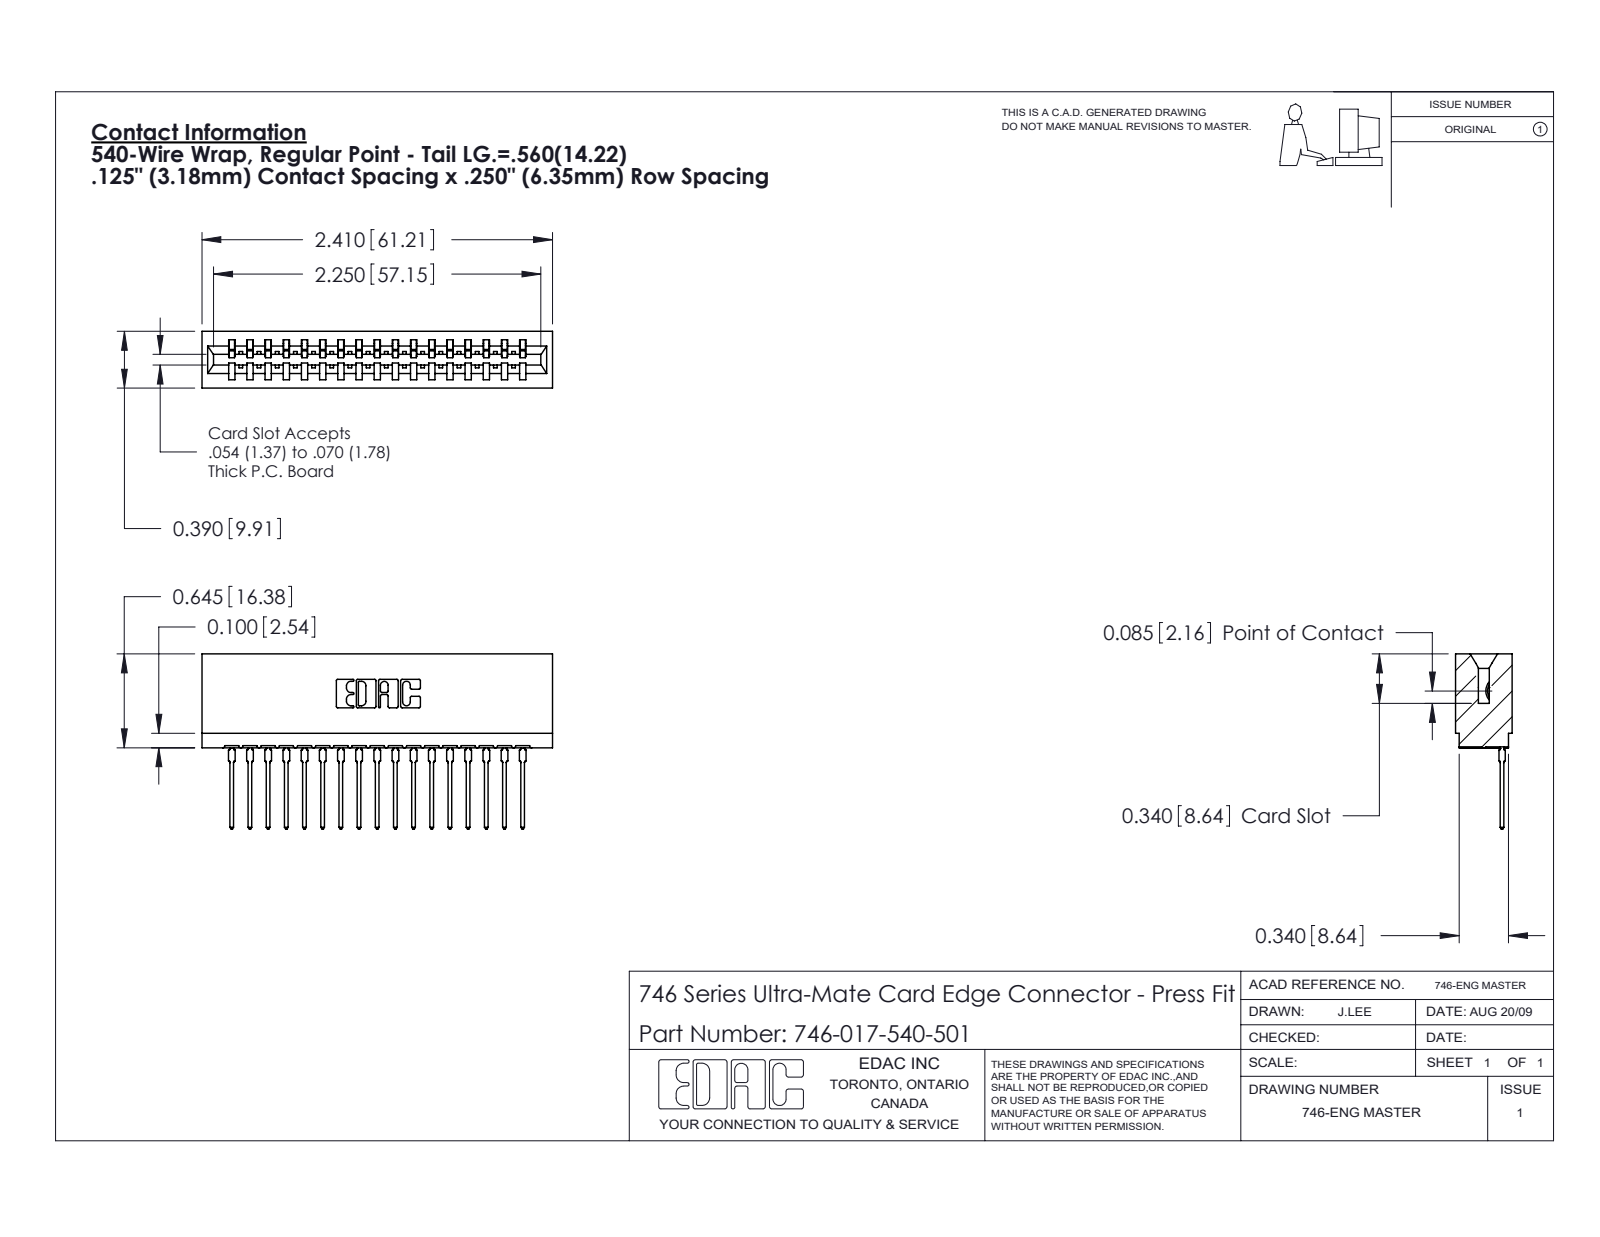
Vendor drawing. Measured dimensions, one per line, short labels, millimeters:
name: 746-017-540-501; 746 Part_.340 Slot Depth - 01; 746-292-001_540
written by: SolidWorks 2020 (CONFIG_CONTROL_DESIGN)
unit: mm
bodies: 18 solids, 1933 faces (1126 planar, 365 cylindrical, 442 other)
size: 61.2 × 30.6 × 9.9
volume: 7 060 mm³; area: 9 355 mm²
rounds: 34× R0.5, 22× R0.3, 18× R0.4, 6× R0.2, 6× R0.8, 4× R0.1, 4× R0.3, 3× R0.7
face distances: 6.4, 1.4, 8.5, 9.9, 12.7, 0.6, 7.8, 1.1, 7.4, 9.5
